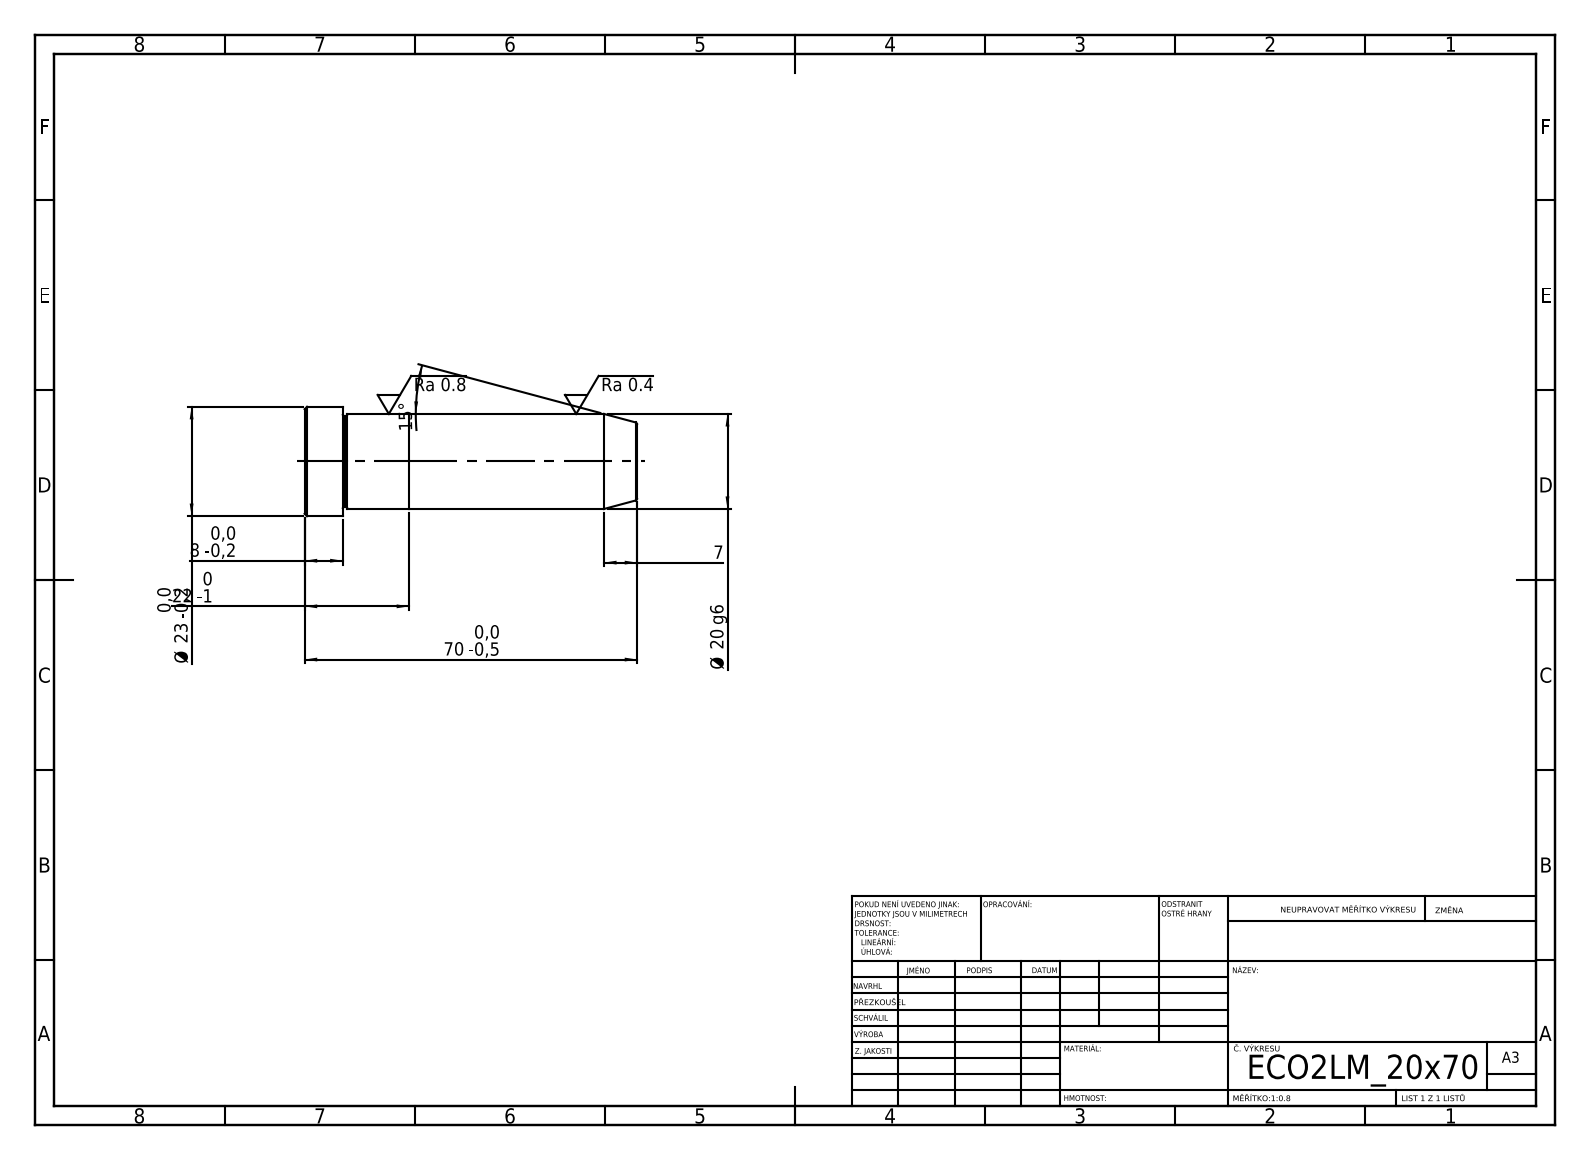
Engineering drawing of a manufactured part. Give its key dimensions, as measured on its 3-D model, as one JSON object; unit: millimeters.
{"step_written_by": "SolidWorks 2019 (CONFIG_CONTROL_DESIGN)", "units": "millimeters", "bodies": {"solids": 2, "faces": 21, "planar": 5, "cylindrical": 6, "other": 10}, "overall_size": [70, 23, 23], "volume_mm3": 22381, "surface_area_mm2": 5804, "round_bosses_or_shafts": [[23, 1], [20, 1]], "face_to_face_distances": [22, 48, 70, 62, 14, 8]}
